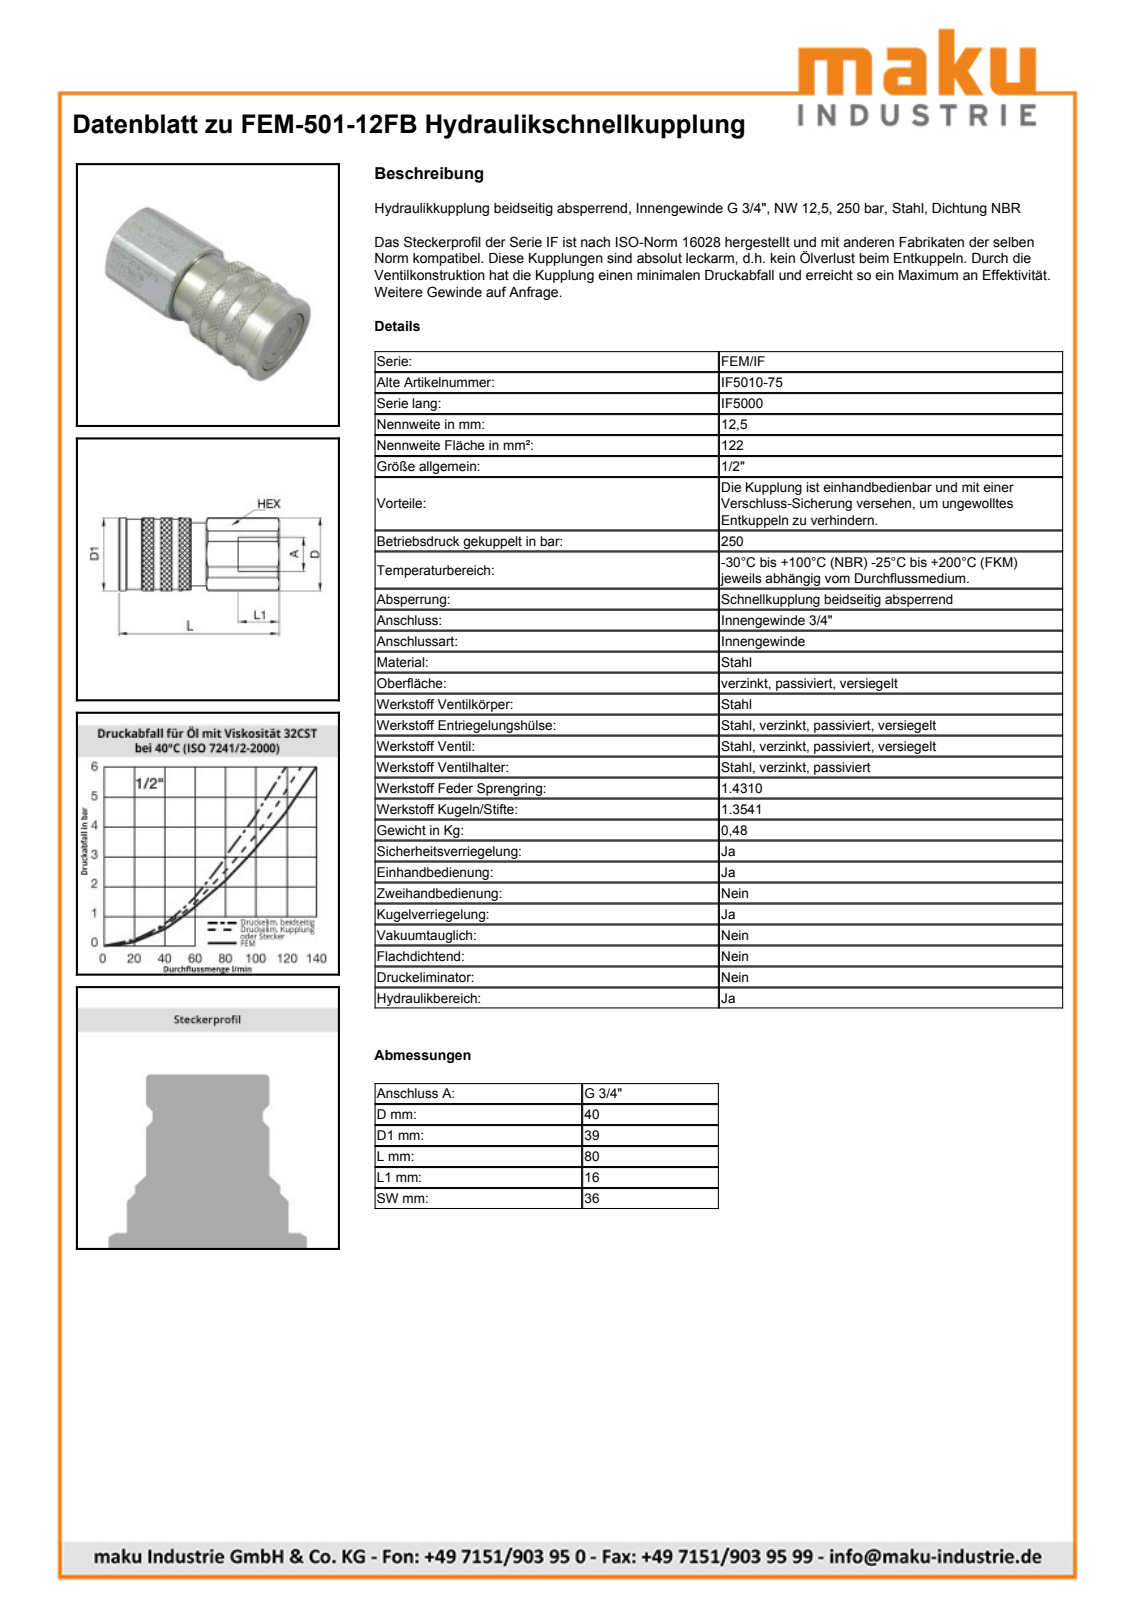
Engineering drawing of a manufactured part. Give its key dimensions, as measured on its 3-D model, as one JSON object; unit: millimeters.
{"part_name": "FEM-501-12FB", "step_written_by": "SolidWorks 2009 (AUTOMOTIVE_DESIGN)", "units": "millimeters", "bodies": {"solids": 2, "faces": 233, "planar": 38, "cylindrical": 75, "other": 120}, "overall_size": [79.9, 40, 38], "volume_mm3": 89421, "surface_area_mm2": 26244, "round_holes": [[2, 1], [15.75, 1], [24.12, 1], [24.7, 1], [25.5, 1], [30.7, 1], [34.4, 1]], "round_bosses_or_shafts": [[38, 1], [36.7, 1], [34.2, 1], [34, 1], [32.6, 1], [30, 1], [28.6, 1], [28.2, 1]], "partial_cylinders_radius": [[0.5, 2], [20, 1]], "face_to_face_distances": [36, 79.9, 79.6, 19.76, 59.84, 60.14, 79.28, 59.52, 0.32, 0.62]}
